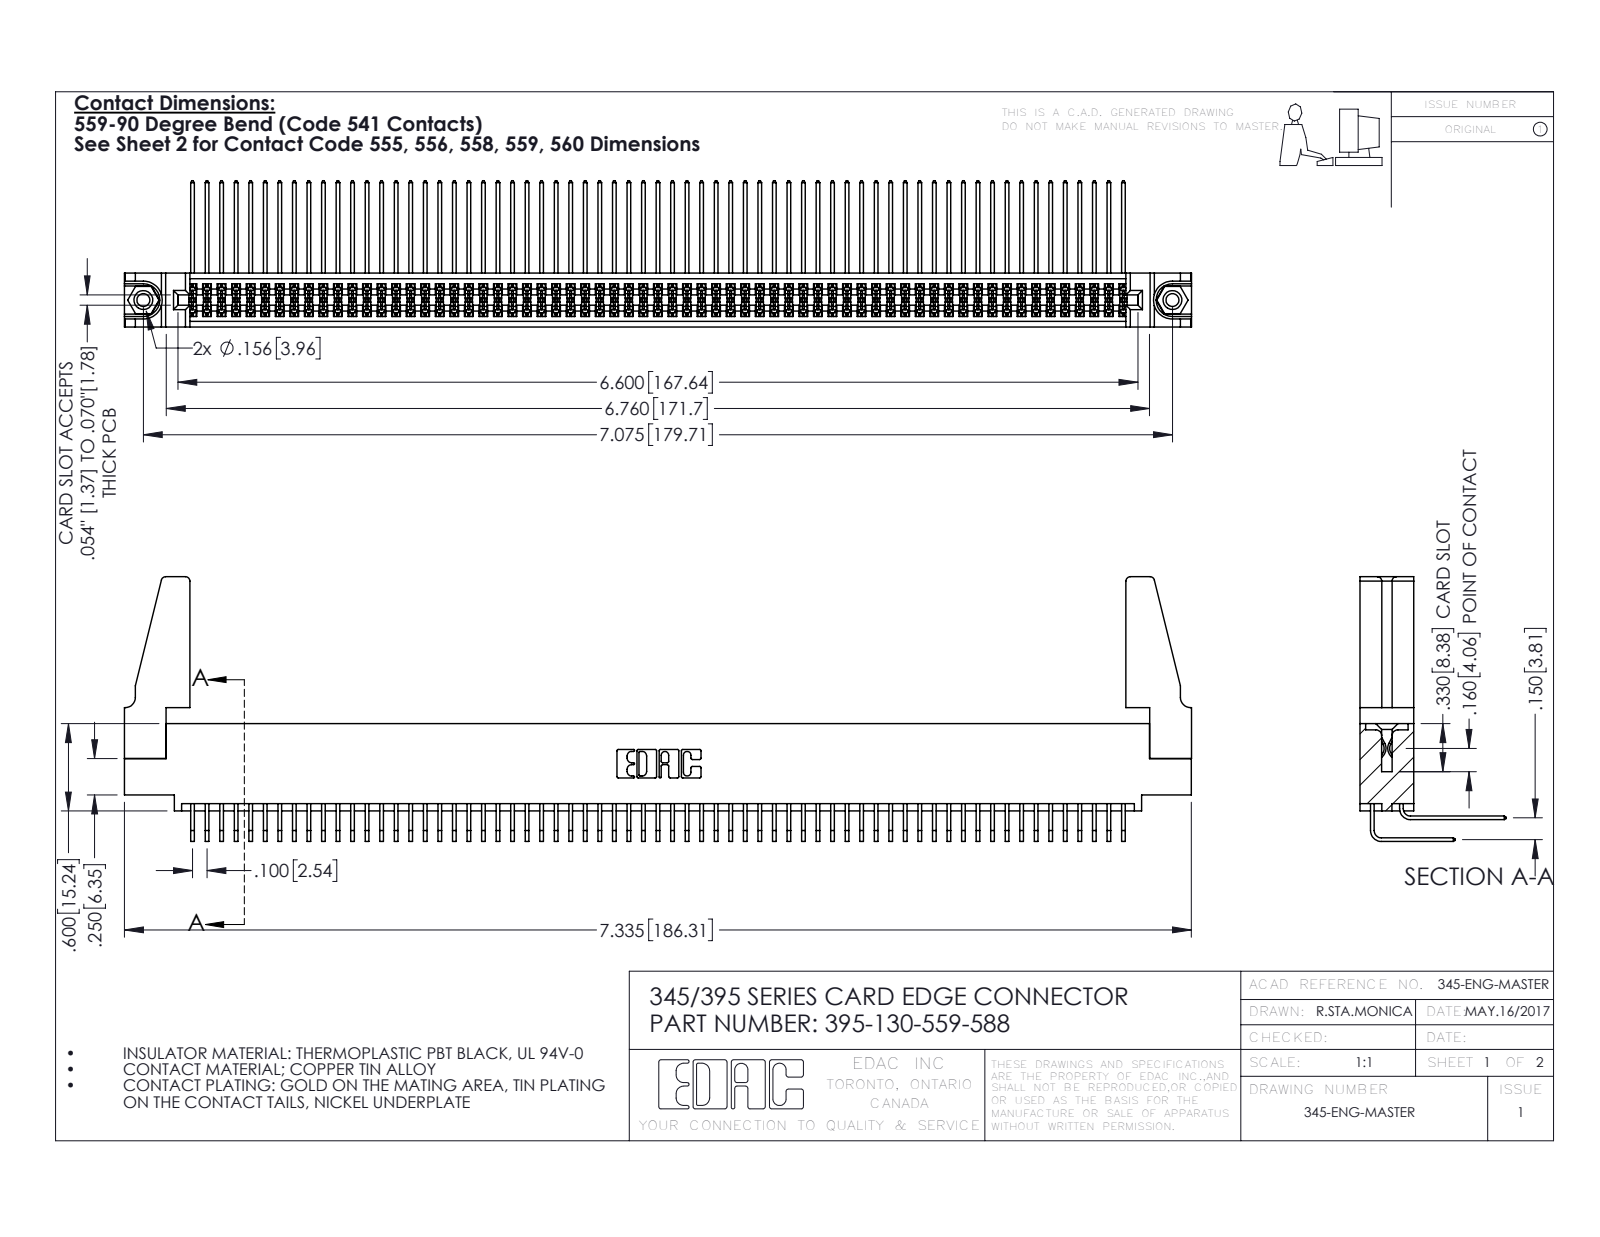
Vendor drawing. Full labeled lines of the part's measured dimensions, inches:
Part name (STEP PRODUCT): 345-220-078_345-220-088; 345-292-001_559 Tail - 2; 345-292-001_558 559 Tail - 1; 345 Part_0.110 Offset - 0.156 Dia-TH (+2 more)
STEP written by: SolidWorks 2016 (CONFIG_CONTROL_DESIGN)
Units: inches
Bodies: 135 solids, 7014 faces (4706 planar, 2292 cylindrical, 16 other)
Overall size (bounding box): 7.336 × 1.819 × 1.005
Volume: 1.357 in³ · Surface area: 54.65 in²
Round holes (diameter × count): ⌀0.089 ×2, ⌀0.125 ×2, ⌀0.156 ×2, ⌀0.064 ×1
Round bosses / shafts (diameter × count): ⌀0.155 ×2
Partial cylindrical surfaces — rounded edges, fillets, slot ends (radius × count): R0.006 ×196, R0.01 ×22, R0.03 ×8, R0.007 ×6, R0.031 ×6, R0.026 ×3, R0.014 ×2, R0.019 ×2
Main face-to-face distances: 0.072, 0.298, 0.37, 0.2, 0.098, 0.272, 0.025, 0.225, 0.175, 0.15
Hole centre spacings: 0.27, 6.839, 7.075
